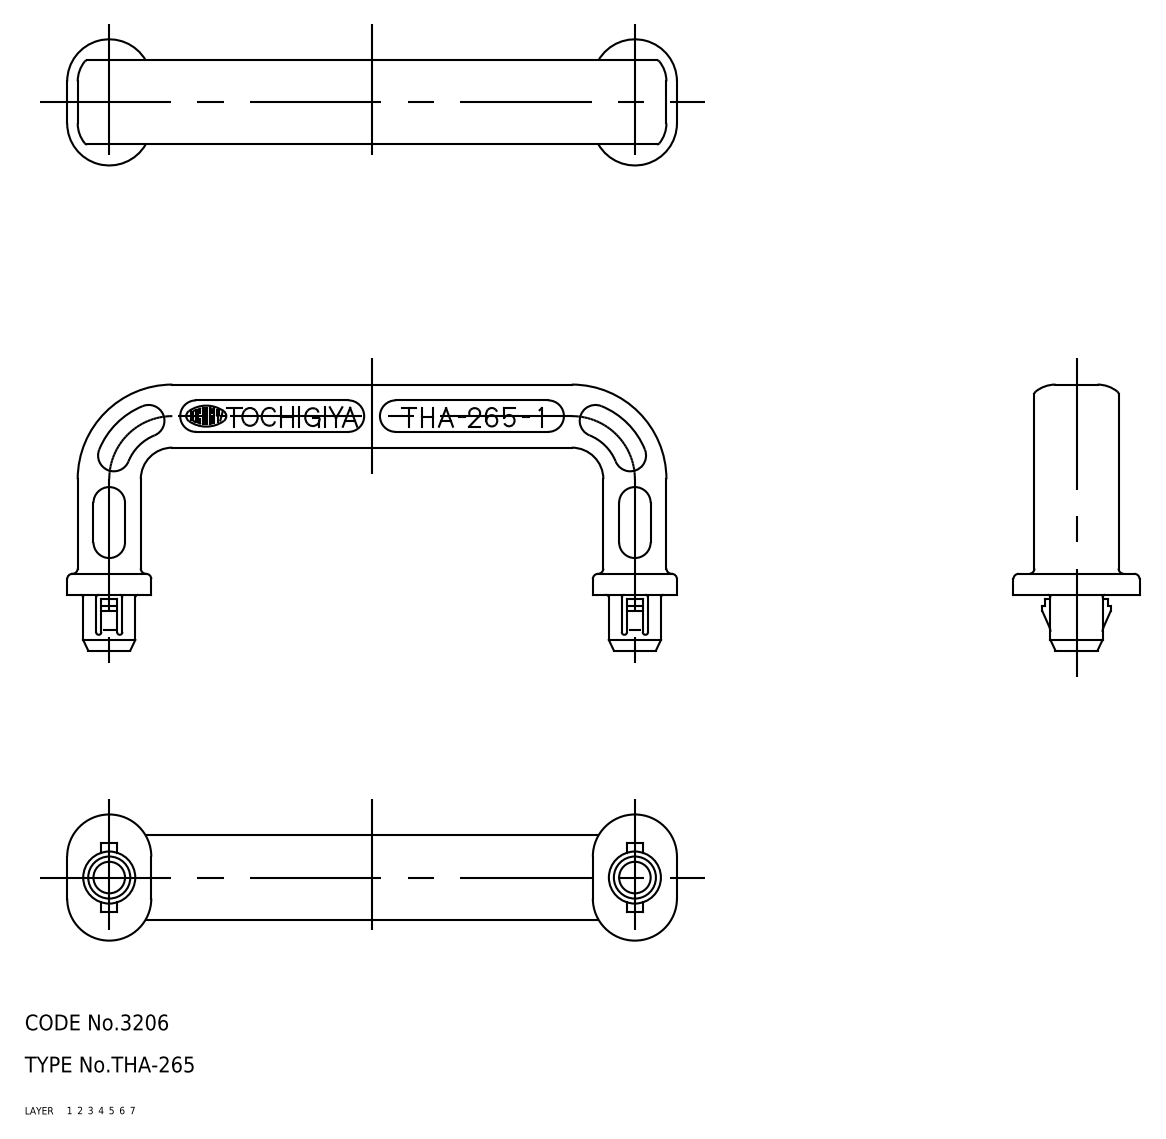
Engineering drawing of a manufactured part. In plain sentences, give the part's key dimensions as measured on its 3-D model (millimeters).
The part is named "pull". Its 3-D file was written by "CADfix (AUTOMOTIVE_DESIGN)". It is 1 solid with 224 faces: 0 planar, 0 cylindrical and 224 other. Overall it measures 116 by 50.6 by 24 millimeters. Its volume is 22 229 cubic millimeters and its surface area 14 089 square millimeters.
